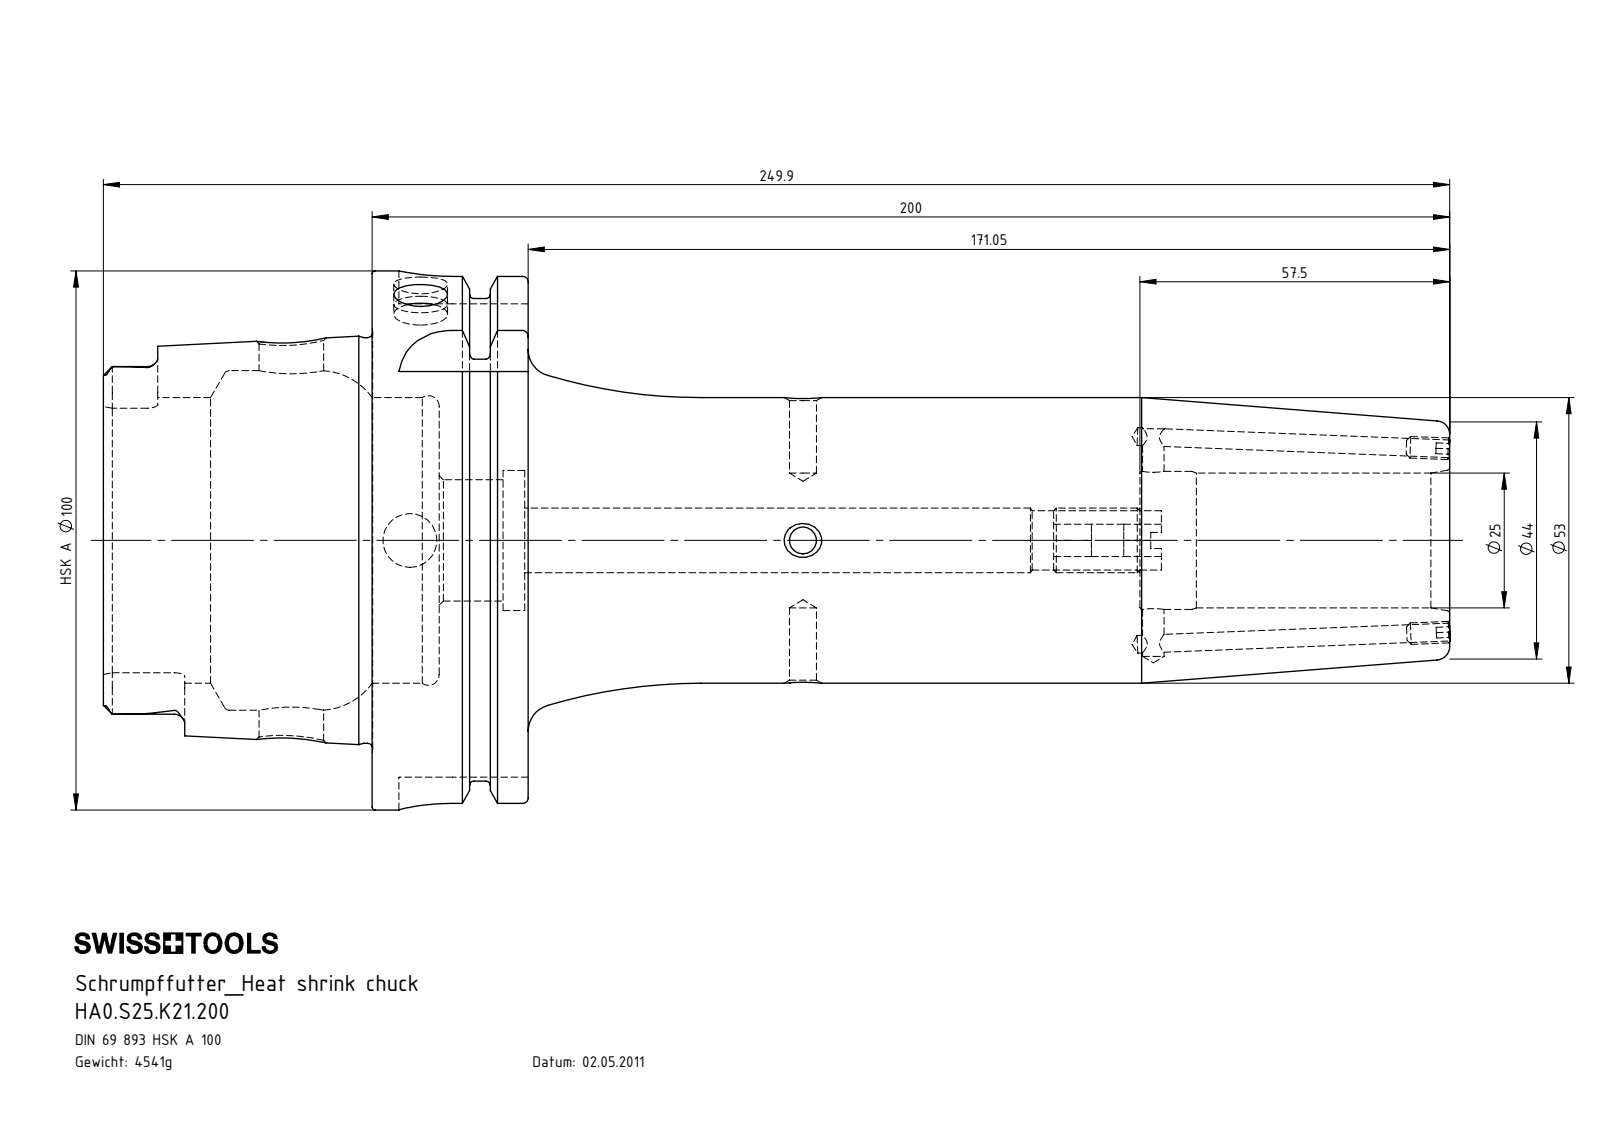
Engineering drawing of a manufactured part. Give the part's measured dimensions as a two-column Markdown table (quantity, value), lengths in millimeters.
| quantity | value |
| --- | --- |
| part name | ERU-CJ3.001.008; ERU-AN5.K01.020_A; HA0-S25.K21.200_D_Fertigbearbeitung; HA0.S25.K21.200 |
| STEP written by | SolidWorks 2017 (CONFIG_CONTROL_DESIGN) |
| units | millimeters |
| bodies | 4 solids, 304 faces (95 planar, 89 cylindrical, 120 other) |
| overall size | 250 × 100 × 100 |
| volume | 578 486 mm³ |
| surface area | 88 321 mm² |
| round holes (diameter × count) | 10 × 3, 3.3 × 2, 5 × 2, 12 × 2, 4 × 1, 6 × 1, 11 × 1, 22.5 × 1, 25 × 1, 25.6 × 1, 26 × 1, 53 × 1 |
| round bosses / shafts (diameter × count) | 4 × 2, 100 × 1, 91.95 × 1, 75.26 × 1 |
| partial cylindrical surfaces (radius × count) | 1.9 × 6, 4.88 × 4, 10 × 4 |
| main face-to-face distances | 28.95, 12.45, 16.5, 49.9, 62.35, 78.85, 249.9, 200, 187.55, 171.05 |
| hole center spacings | 65.05, 72.95, 94.95, 160 |
